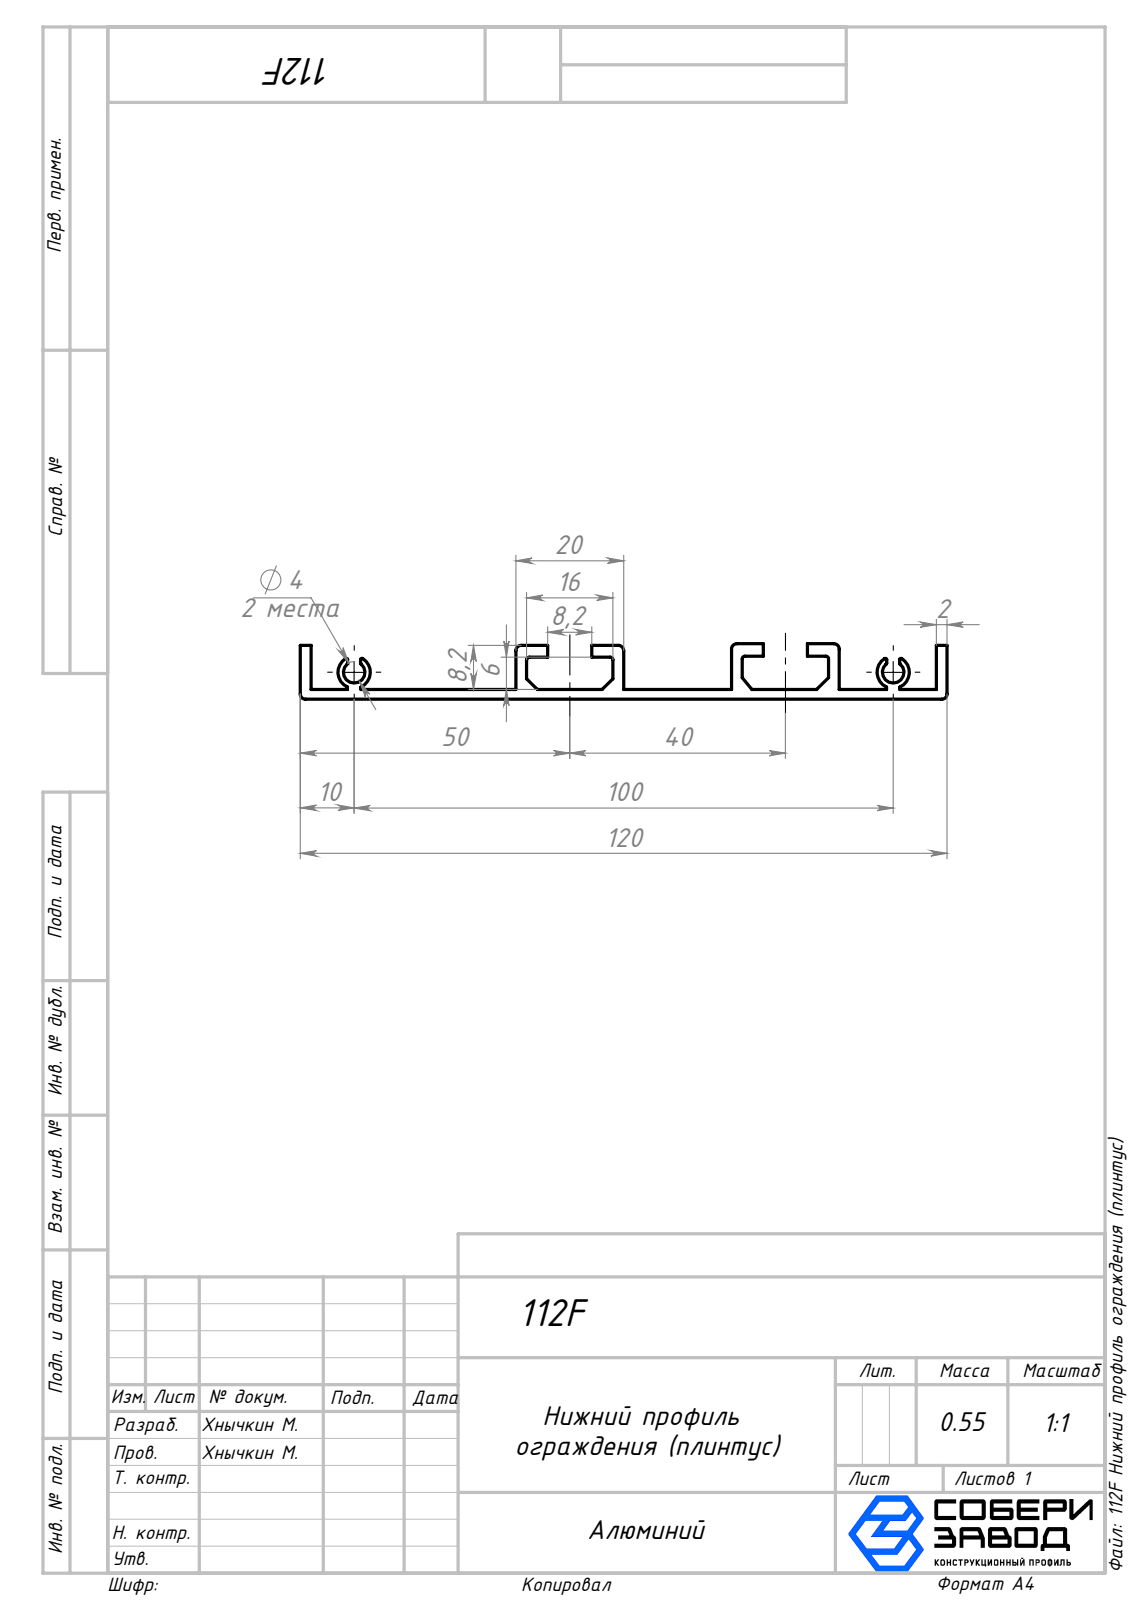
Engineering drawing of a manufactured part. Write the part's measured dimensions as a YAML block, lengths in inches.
part_name: "112F Нижний профиль ограждения (плинтус)"
step_written_by: "SolidWorks 2026 (AUTOMOTIVE_DESIGN)"
units: inches
bodies: {solids: 1, faces: 78, planar: 48, cylindrical: 30, other: 0}
overall_size: [20.827, 4.724, 0.406]
volume: 12.45
surface_area: 340.6
partial_cylinders:
  - {radius: 0.01, count: 8}
  - {radius: 0.039, count: 6}
  - {radius: 0.02, count: 4}
  - {radius: 0.079, count: 2}
  - {radius: 0.118, count: 2}
face_to_face_distances: [0.071, 1.575, 0.079, 0.787, 1.496, 2.362, 2.283, 0.709, 0.323, 3.15]
